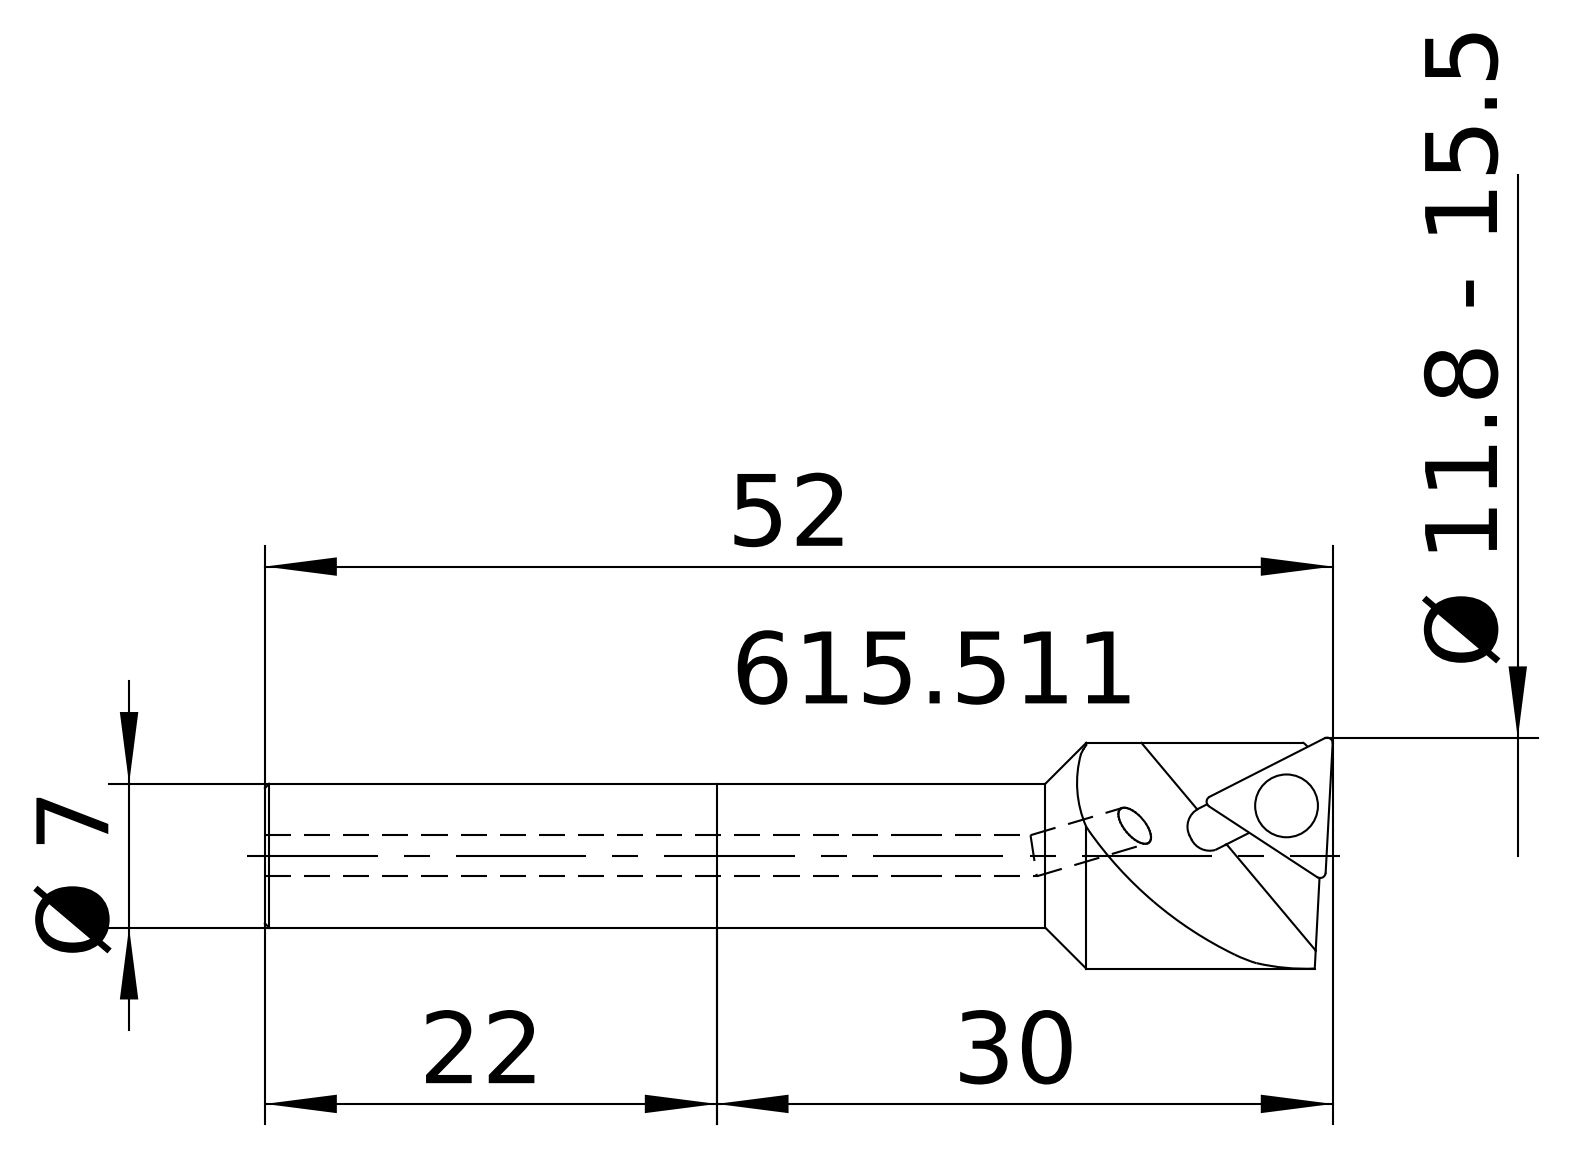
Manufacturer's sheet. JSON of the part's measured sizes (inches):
{"part_name": "615.511 Kaiser E12 TP07 x 52HM|694.103 Kaiser ETL M2x4.8 T6 IP 10S;Kreismuster1; 615.511 Kaiser E12 TP07 x 52HM|651.735 Kaiser TPGT 070203 K10C;Kombinieren1; 615.511 Kaiser E12 TP07 x 52HM|615.511 Kaiser E12 TP07 x 52HM;Schnitt-Rotation4", "step_written_by": "ACIS (automotive_design)", "units": "inches", "bodies": {"solids": 3, "faces": 100, "planar": 28, "cylindrical": 39, "other": 33}, "overall_size": [2.031, 0.443, 0.433], "volume_in3": 0.132, "surface_area_in2": 2.785, "round_holes": [[0.079, 2], [0.061, 1], [0.091, 1]], "round_bosses_or_shafts": [[0.433, 1], [0.276, 1], [0.106, 1], [0.079, 1]], "partial_cylinders_radius": [[0.006, 6], [0.012, 6], [0.039, 1], [0.039, 1], [0.118, 1]], "face_to_face_distances": [0.098, 0.086, 0.068, 0.03, 0.091, 0.159, 0.189, 0.28, 0.198, 2.019]}
